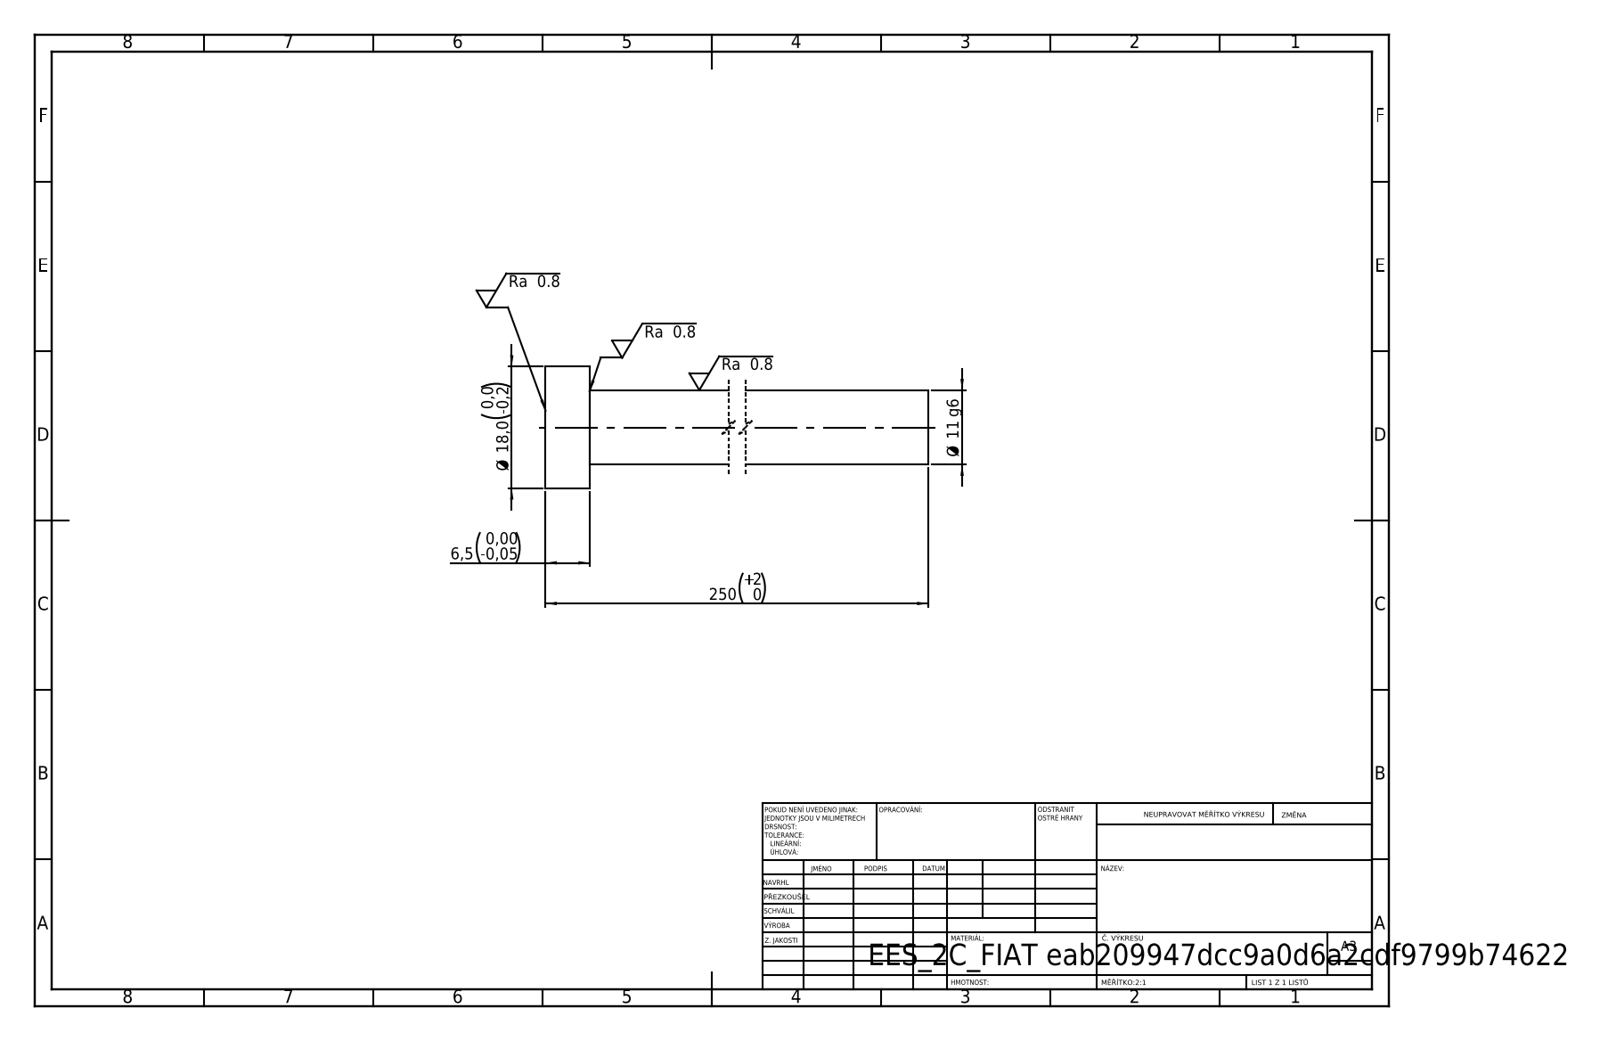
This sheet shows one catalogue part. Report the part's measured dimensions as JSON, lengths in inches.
{"step_written_by": "SolidWorks 2019 (CONFIG_CONTROL_DESIGN)", "units": "inches", "bodies": {"solids": 1, "faces": 7, "planar": 3, "cylindrical": 4, "other": 0}, "overall_size": [9.843, 0.709, 0.709], "volume_in3": 1.513, "surface_area_in2": 14.4, "round_bosses_or_shafts": [[0.709, 1], [0.433, 1]], "face_to_face_distances": [0.256, 9.843, 9.587]}
